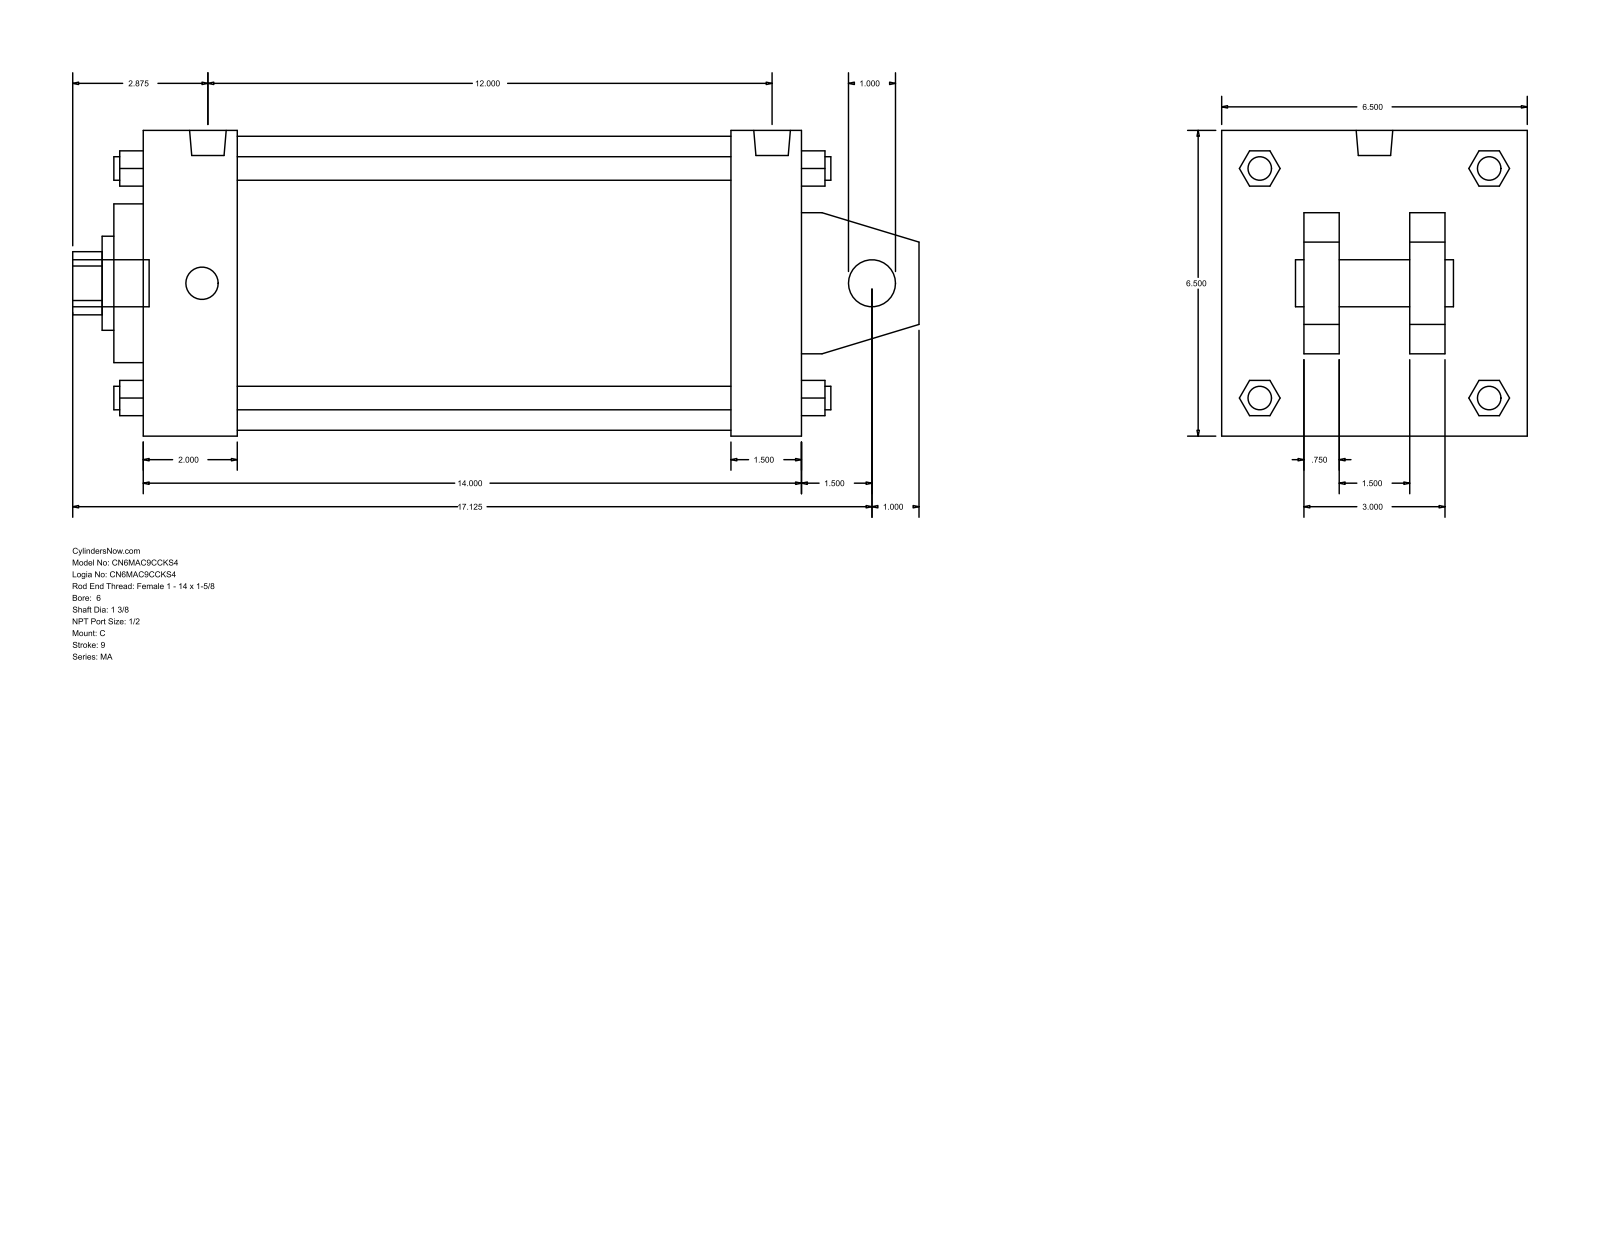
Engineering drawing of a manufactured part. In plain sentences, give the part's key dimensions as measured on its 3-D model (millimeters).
The part is named "MA_C__0600_1.375". Its 3-D file was written by "GSSL Pune (CONFIG_CONTROL_DESIGN)". It is 0 solids with 141 faces: 109 planar, 32 cylindrical and 0 other. Overall it measures 457.2 by 165.1 by 165.1 millimeters. Round holes: 1 of diameter 25.4, 1 of diameter 34.92, 1 of diameter 50.8, 1 of diameter 85.72, 1 of diameter 158.75. Round bosses or shafts: 4 of diameter 17.46, 4 of diameter 12.7, 2 of diameter 19.77, 1 of diameter 25.4. Partial cylindrical surfaces (rounded edges, fillets, slot ends): 1 of radius 17.06. The main face-to-face distances are 165.1, 355.6, 38.1, 19.05, 63.5, 101.6, 50.8, 120.65, 44.45, 317.5.
